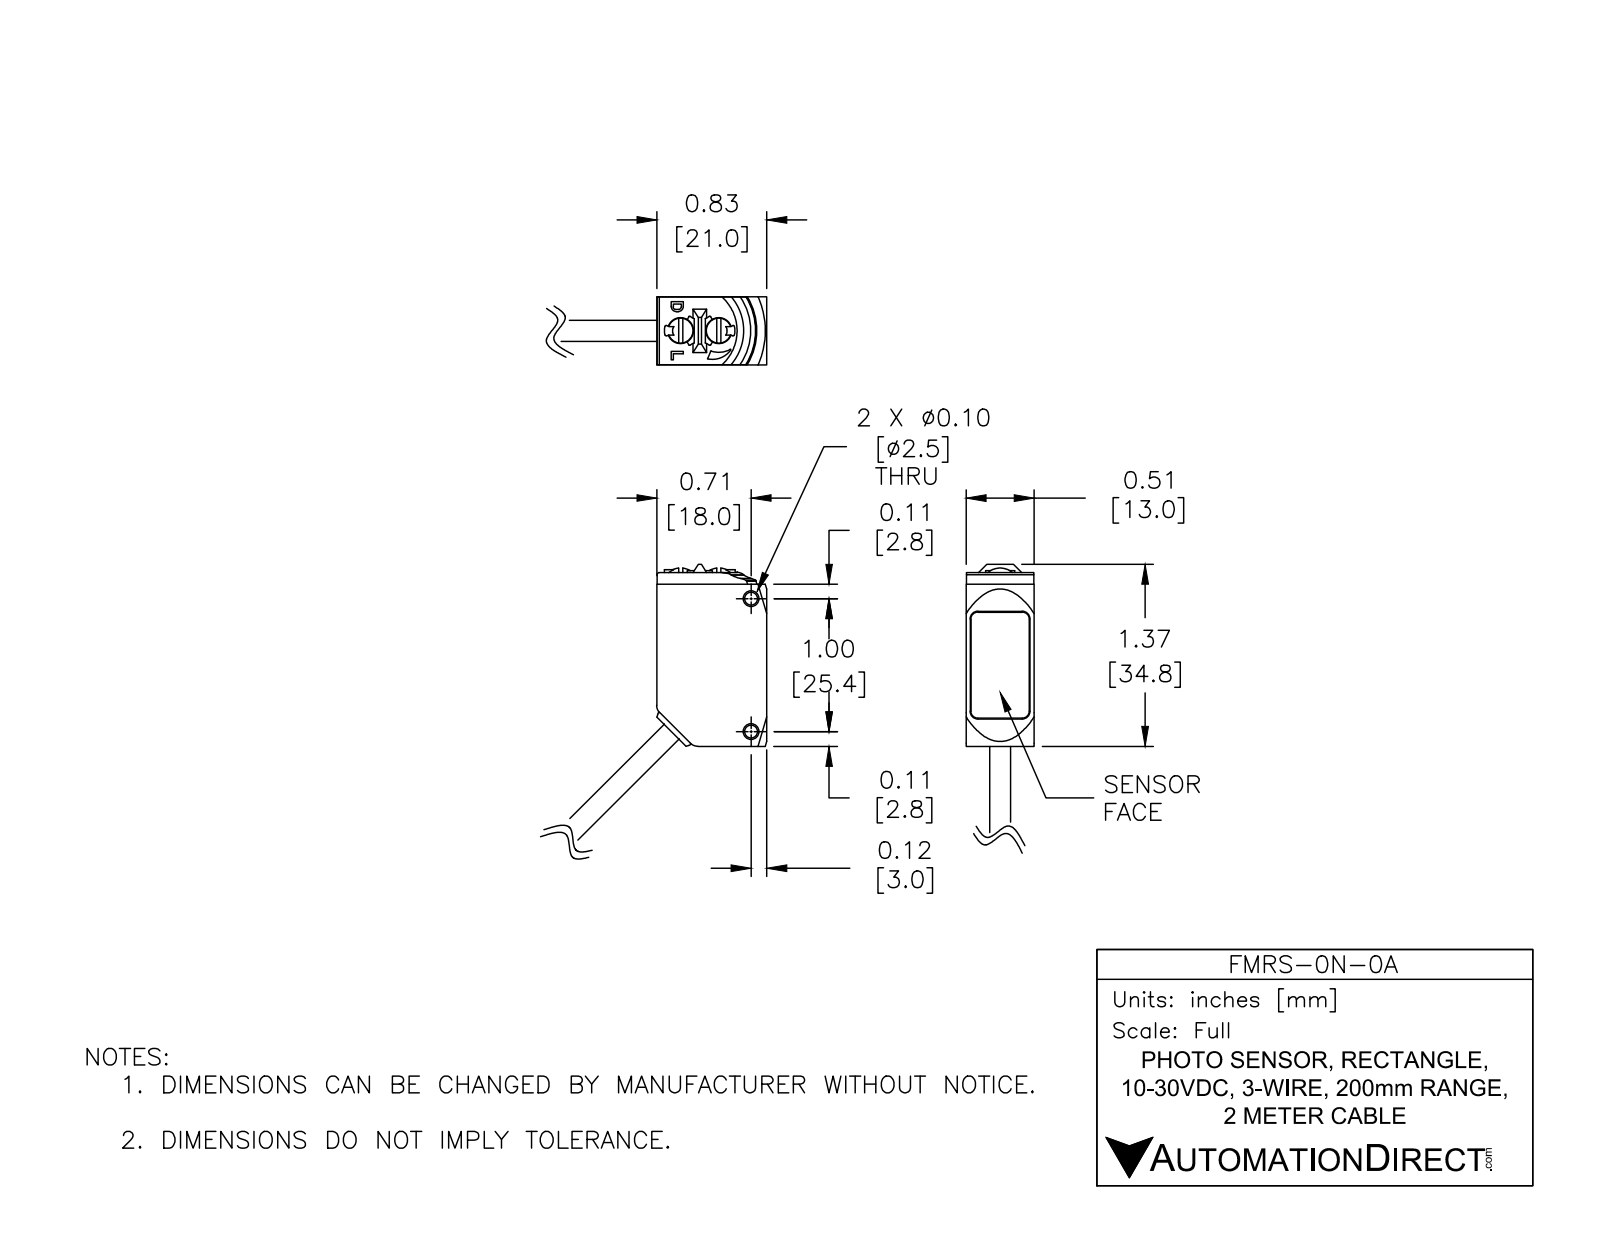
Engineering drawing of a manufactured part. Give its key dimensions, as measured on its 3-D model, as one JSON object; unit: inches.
{"part_name": "FMRS-0N-0A", "step_written_by": "SolidWorks 2017 (AUTOMOTIVE_DESIGN)", "units": "inches", "bodies": {"solids": 1, "faces": 186, "planar": 89, "cylindrical": 72, "other": 25}, "overall_size": [2.084, 1.541, 0.512], "volume_in3": 0.542, "surface_area_in2": 5.476, "round_holes": [[0.097, 2], [0.197, 2]], "round_bosses_or_shafts": [[0.189, 2], [0.157, 1]], "partial_cylinders_radius": [[0.018, 7], [0.02, 7], [0.008, 4], [0.01, 4], [0.051, 4], [0.059, 4], [0.004, 3], [0.018, 2]], "face_to_face_distances": [0.512, 0.827, 1.307, 0.035, 0.51, 0.031, 0.48, 0.037, 0.474, 0.472], "hole_center_spacings": [0.287, 1]}
